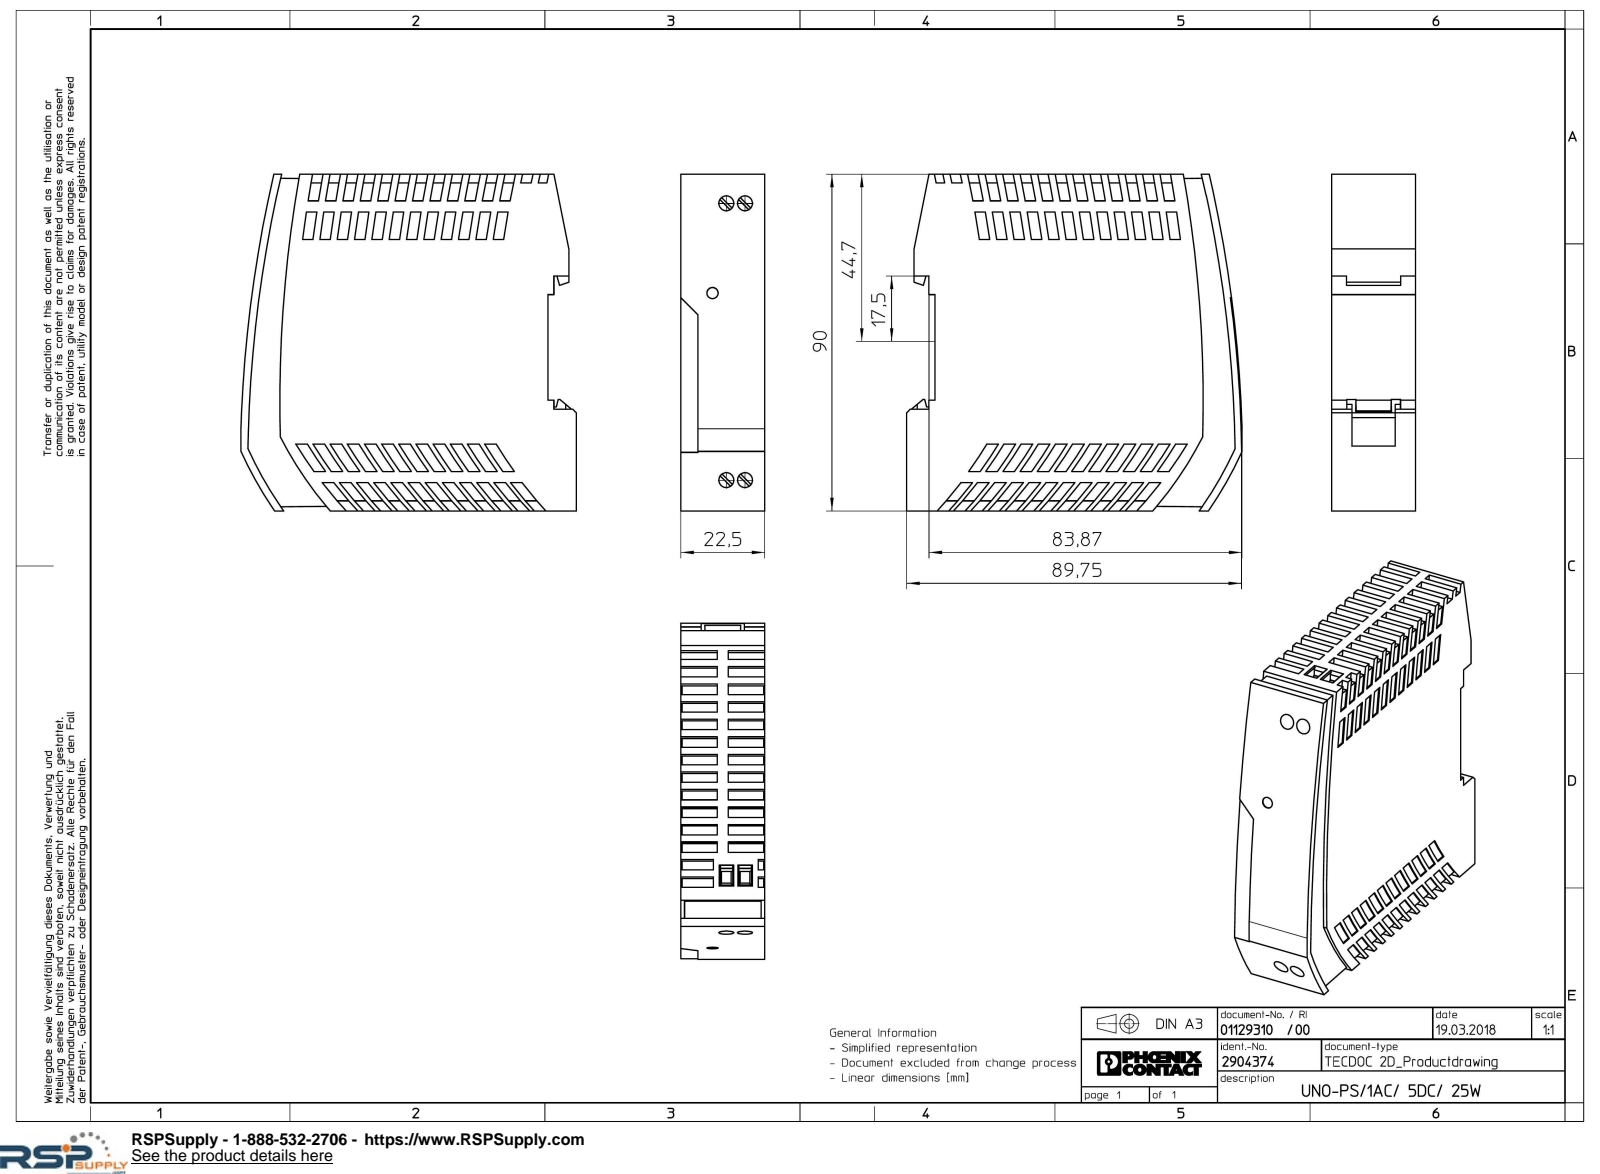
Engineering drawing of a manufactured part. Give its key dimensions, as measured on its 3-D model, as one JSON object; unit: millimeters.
{"part_name": "UNO_PS_1AC_5DC_25W-select", "step_written_by": "Creo Elements/Direct Modeling 20.1A 29-Sep-2018 (C) Parametric Technology GmbH (AUTOMOTIVE_DESIGN)", "units": "millimeters", "bodies": {"solids": 1, "faces": 728, "planar": 511, "cylindrical": 215, "other": 2}, "overall_size": [90, 89.87, 22.5], "volume_mm3": 160983, "surface_area_mm2": 27308, "round_holes": [[4, 4]], "partial_cylinders_radius": [[111, 26], [98, 1], [98.55, 1], [100, 1], [282.66, 1], [284.9, 1], [286.76, 1], [291.36, 1]], "face_to_face_distances": [22.5, 22.2, 1, 0.7, 21.5, 21.2, 21.9, 90, 2.7, 87.3], "hole_center_spacings": [5, 74, 74.17]}
